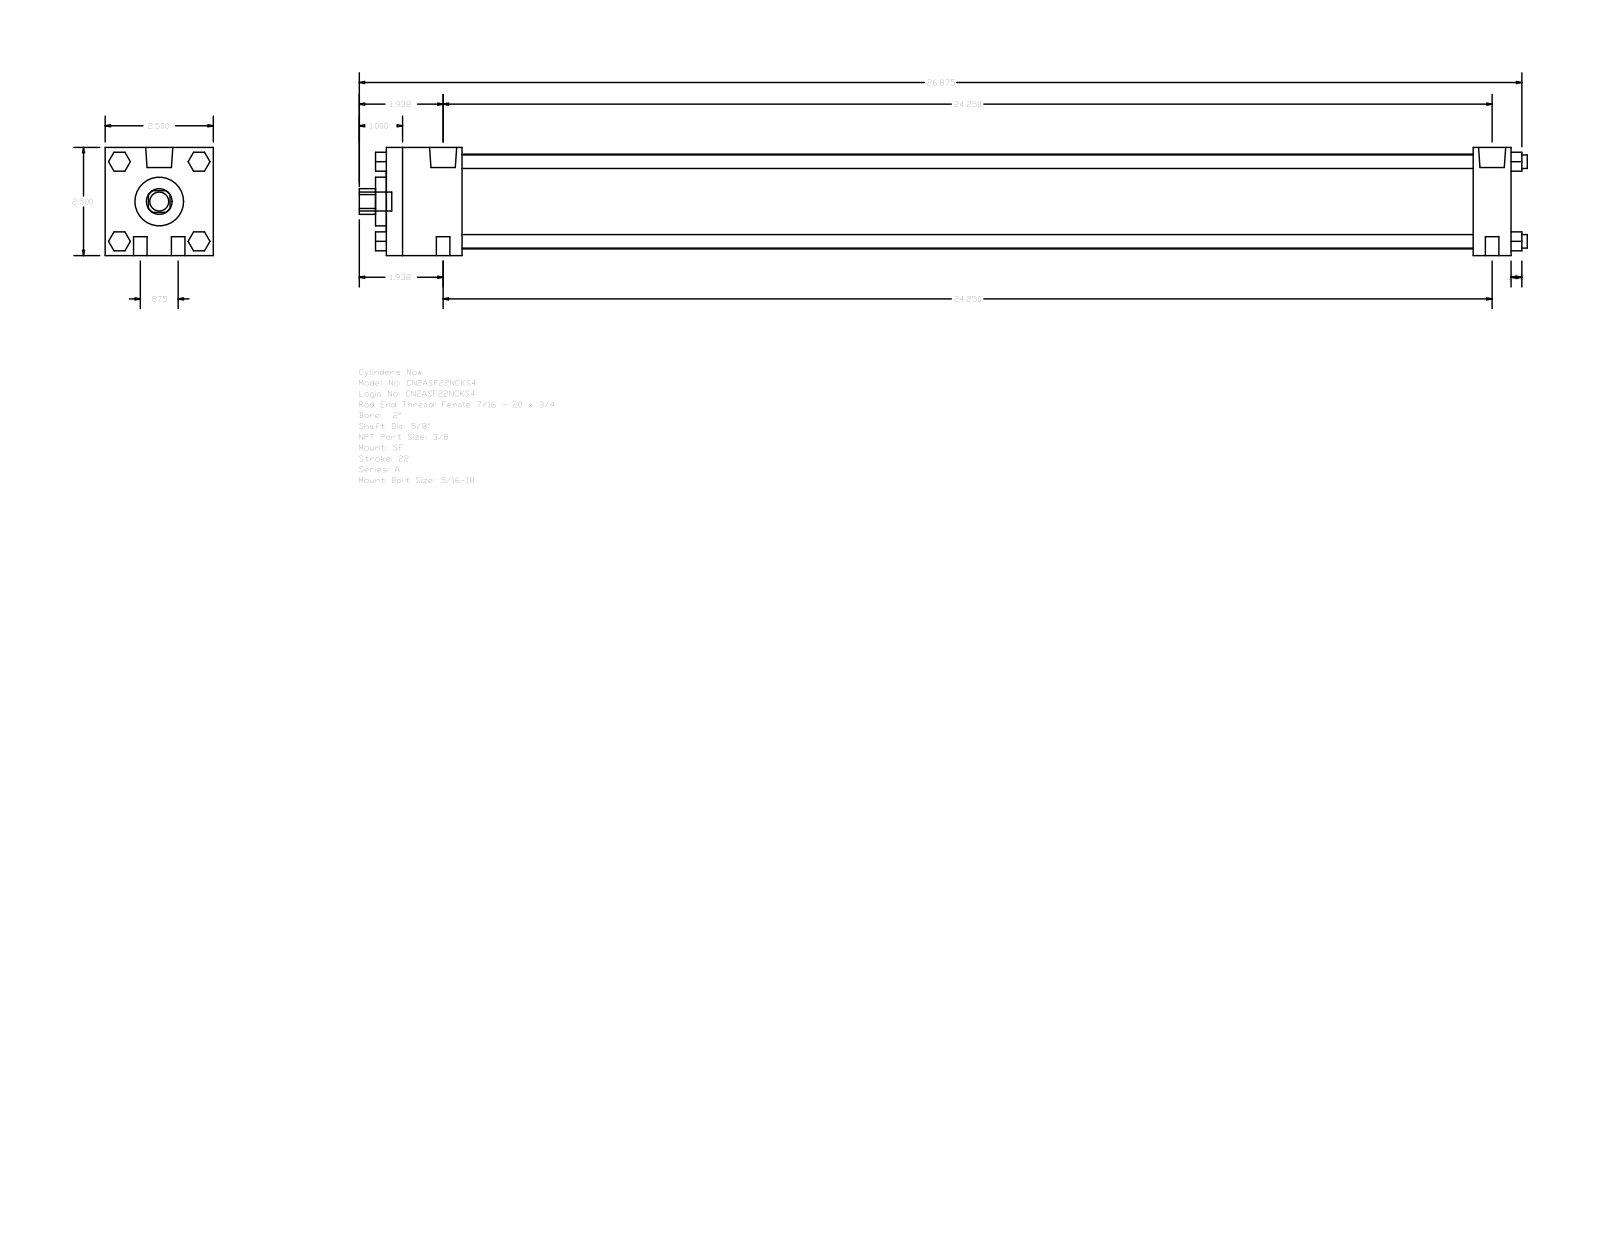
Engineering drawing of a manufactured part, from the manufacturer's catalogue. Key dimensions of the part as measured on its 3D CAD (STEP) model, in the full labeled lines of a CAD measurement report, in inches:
Part name (STEP PRODUCT): A_SF__0200_0.625
STEP written by: GSSL Pune (CONFIG_CONTROL_DESIGN)
Units: inches
Bodies: 0 solids, 124 faces (94 planar, 30 cylindrical, 0 other)
Overall size (bounding box): 27 × 2.5 × 2.5
Round holes (diameter × count): ⌀0.625 ×1, ⌀1.125 ×1, ⌀2.19 ×1
Round bosses / shafts (diameter × count): ⌀0.313 ×8, ⌀0.627 ×2, ⌀0.219 ×2, ⌀0.437 ×1
Partial cylindrical surfaces — rounded edges, fillets, slot ends (radius × count): R0.297 ×1
Main face-to-face distances: 2.5, 26, 25.125, 0.875, 1.75, 23.375, 24.25, 0.25, 26.25, 2
